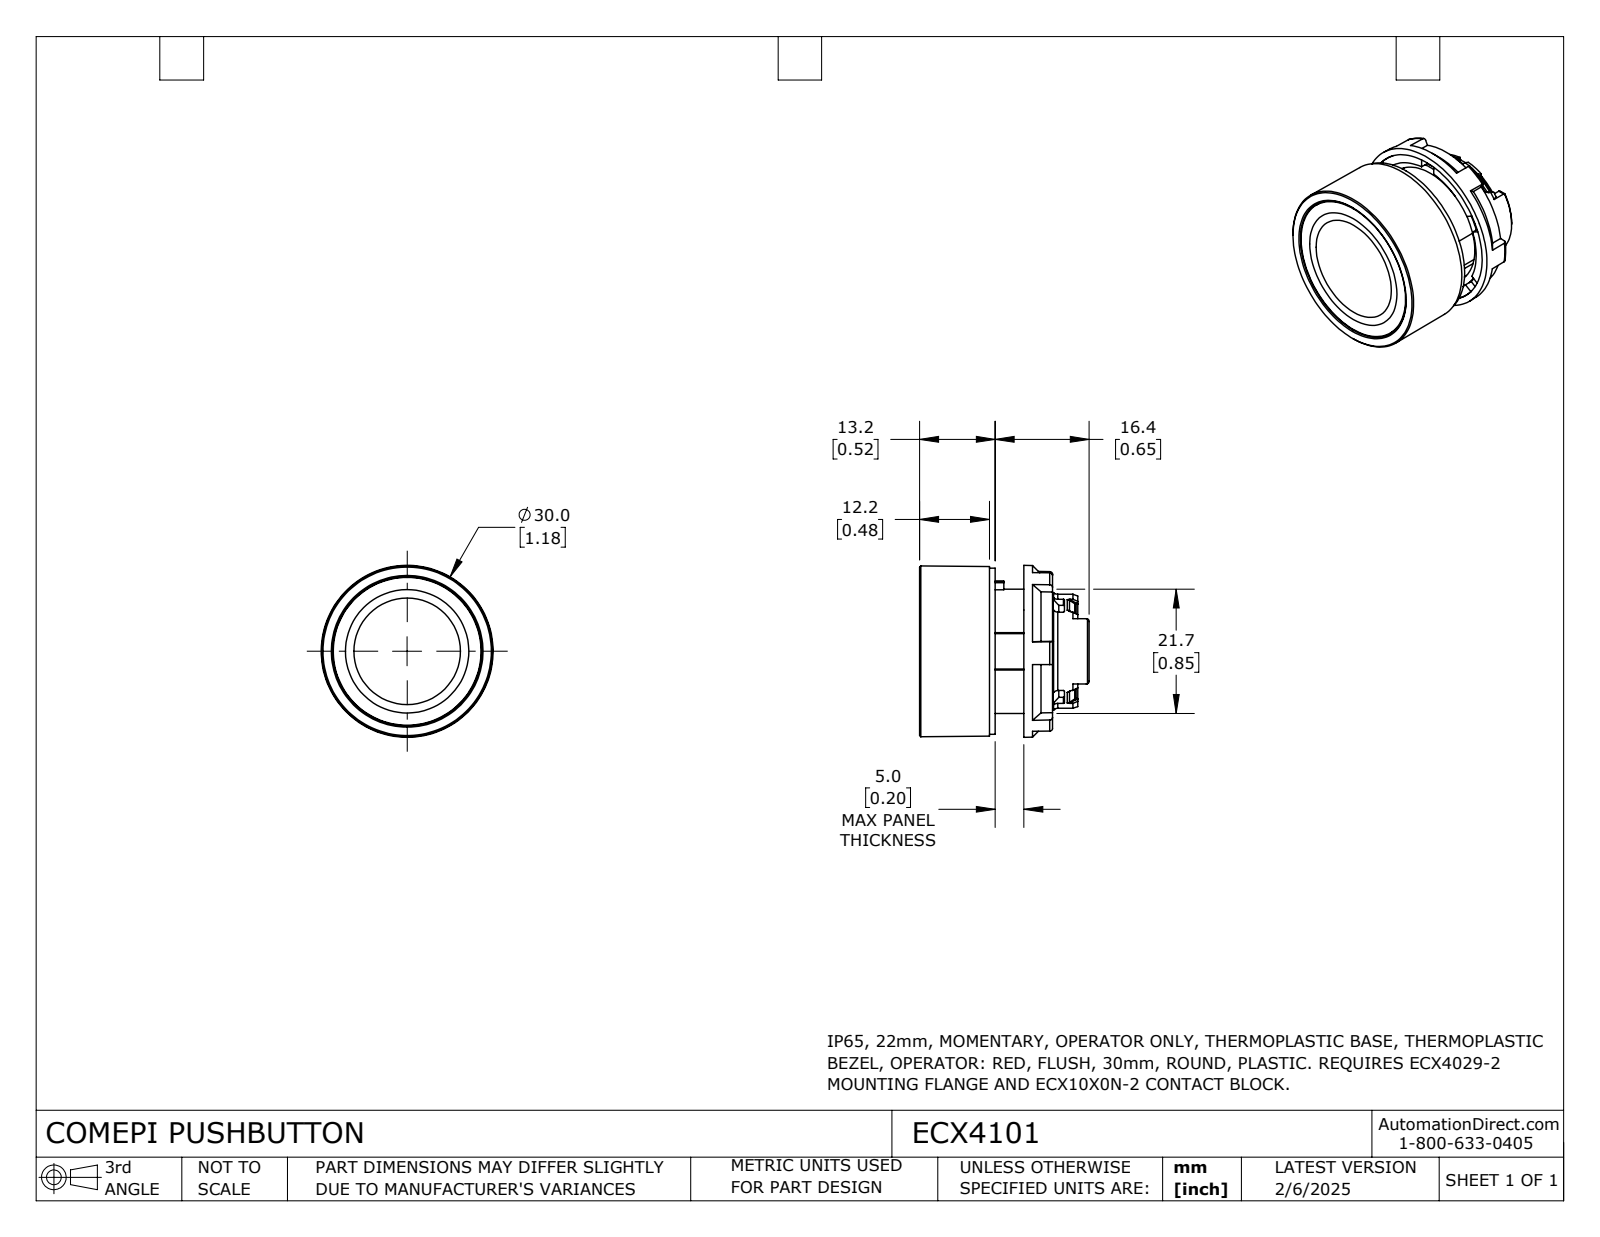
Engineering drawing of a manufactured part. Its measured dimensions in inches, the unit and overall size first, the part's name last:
Units: inches
Overall size (bounding box): 1.181 × 1.181 × 1.165
Round holes (diameter × count): ⌀0.531 ×1, ⌀0.713 ×1, ⌀0.866 ×1
Round bosses / shafts (diameter × count): ⌀1.142 ×1, ⌀1.016 ×1, ⌀0.965 ×1, ⌀0.854 ×1, ⌀0.807 ×1, ⌀0.787 ×1, ⌀0.748 ×1, ⌀0.728 ×1
Partial cylindrical surfaces — rounded edges, fillets, slot ends (radius × count): R0.008 ×24, R0.02 ×8, R0.01 ×2, R0.293 ×1, R0.344 ×1, R0.348 ×1, R0.366 ×1
Main face-to-face distances: 0.409, 0.039, 0.433, 0.472, 0.236, 0.394, 0.197, 0.449, 0.512, 0.217
Volume: 0.472 in³ · Surface area: 16.55 in²
Bodies: 3 solids, 398 faces (134 planar, 111 cylindrical, 153 other)
Part name (STEP PRODUCT): ECX4101
STEP written by: SolidWorks 2024 (CONFIG_CONTROL_DESIGN)
